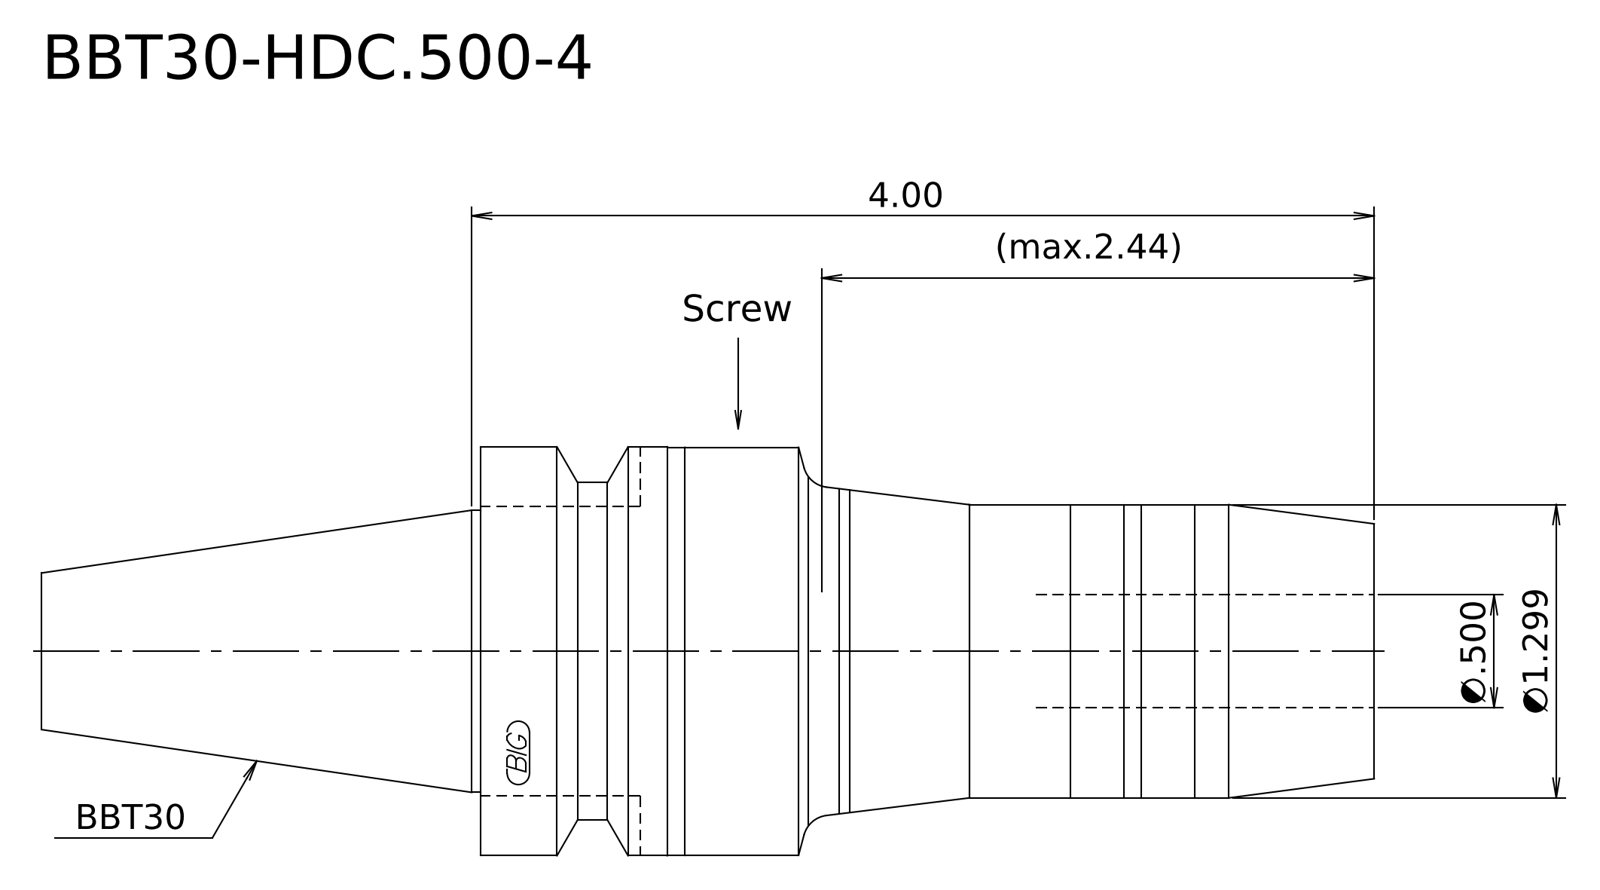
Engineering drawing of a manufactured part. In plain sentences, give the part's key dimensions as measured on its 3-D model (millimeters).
Its 3-D file was written by "Kubotek KeyCreator 2011 V10.0.2 (22737) (automotive_design)". It is 1 solid with 16 faces: 3 planar, 6 cylindrical and 7 other. Overall it measures 150 by 46 by 46 millimeters. Its volume is 137 896 cubic millimeters and its surface area 18 413 square millimeters. Round bosses or shafts: 1 of diameter 46, 1 of diameter 45.9, 1 of diameter 38, 1 of diameter 33, 1 of diameter 31.75. The main face-to-face distances are 100.6, 150, 49.4.
